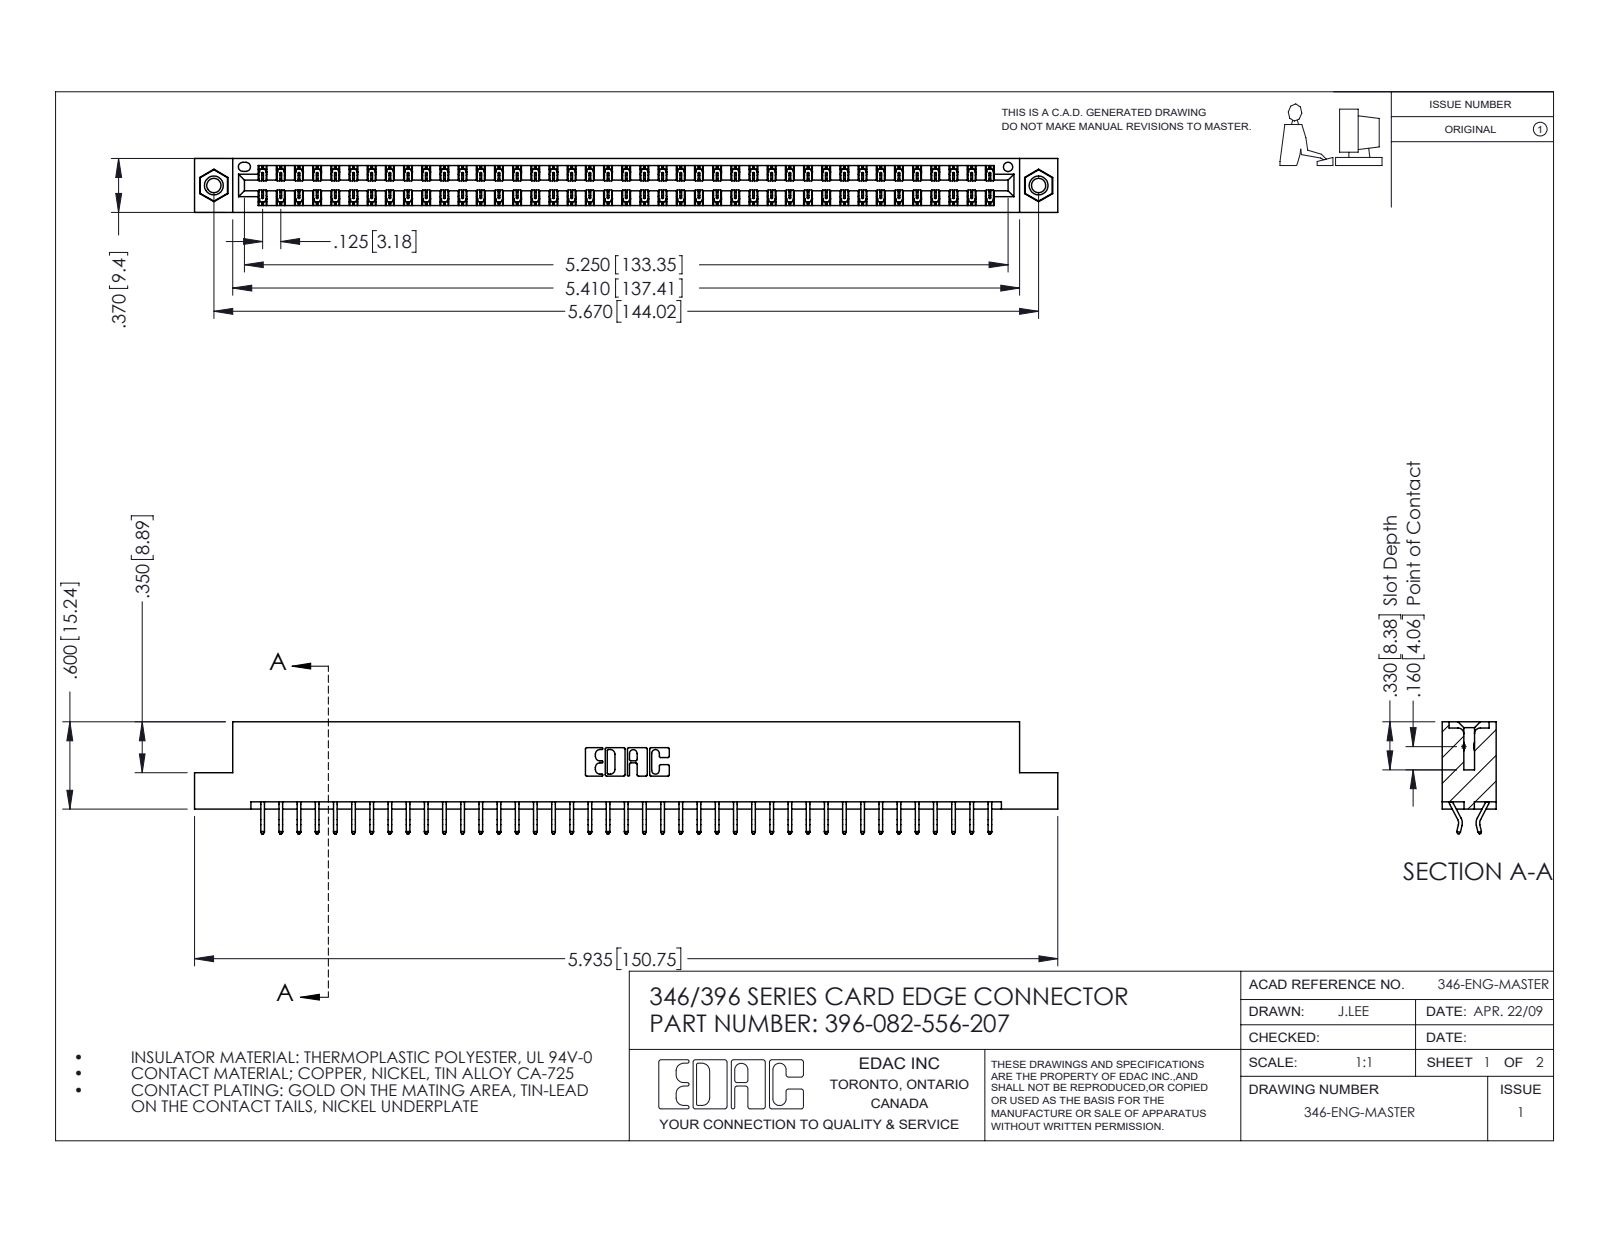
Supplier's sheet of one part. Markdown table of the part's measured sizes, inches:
| quantity | value |
| --- | --- |
| part name | 396-082-556-207; 345-292-001_556 Tail; 346 Part_Flush Mounting Lugs - 0.156 Dia-TI; 345-250-001_345-250-005-103 |
| STEP written by | SolidWorks 2016 (CONFIG_CONTROL_DESIGN) |
| units | inches |
| bodies | 85 solids, 4938 faces (3306 planar, 1616 cylindrical, 16 other) |
| overall size | 5.935 × 0.77 × 0.37 |
| volume | 0.896 in³ |
| surface area | 31.18 in² |
| round holes (diameter × count) | 0.098 × 2, 0.125 × 2, 0.156 × 2, 0.064 × 1 |
| round bosses / shafts (diameter × count) | 0.155 × 2 |
| partial cylindrical surfaces (radius × count) | 0.006 × 123, 0.01 × 22, 0.007 × 6, 0.031 × 6, 0.026 × 3, 0.01 × 2, 0.014 × 2, 0.022 × 2 |
| main face-to-face distances | 0.048, 0.322, 0.37, 0.25, 0.025, 0.072, 0.298, 0.275, 0.148, 0.222 |
| hole center spacings | 0.246, 5.461, 5.67 |
